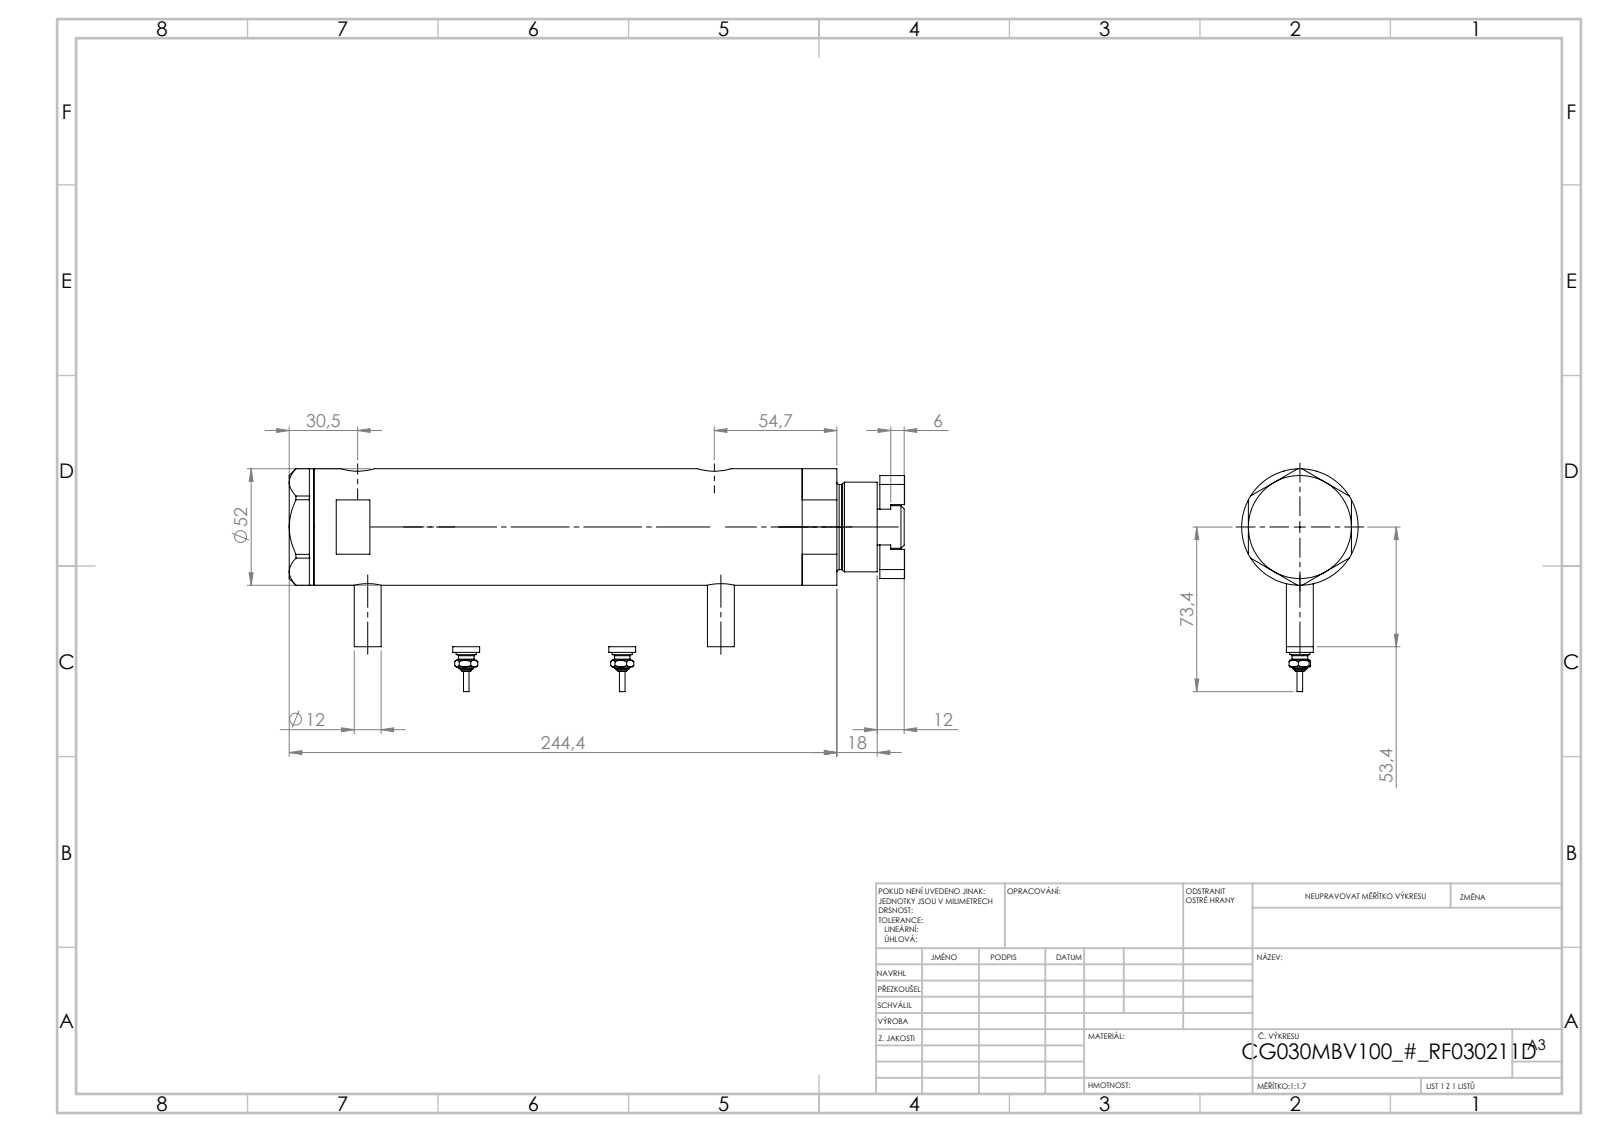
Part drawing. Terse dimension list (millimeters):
name: V270CG_VC; V270CG_BACK; V270CG_SWITCH; V270CG_FRONT (+1 more)
written by: SolidWorks 2019 (CONFIG_CONTROL_DESIGN)
unit: mm
bodies: 6 solids, 246 faces (95 planar, 77 cylindrical, 74 other)
size: 249.02 × 84.3 × 52
volume: 443 477 mm³; area: 99 080 mm²
holes: 2× ⌀5, 2× ⌀9.73, 2× ⌀12.5, 2× ⌀15, 1× ⌀6.5, 1× ⌀20, 1× ⌀21.5, 1× ⌀30, 1× ⌀33, 1× ⌀44
bosses: 3× ⌀12, 2× ⌀9, 2× ⌀7, 2× ⌀4.34, 2× ⌀2.4, 1× ⌀52, 1× ⌀40, 1× ⌀38
face distances: 153.54, 23.8, 129.74, 11, 34.8, 164.54, 46, 200.94, 189.94, 166.14
hole spacings: 2.9, 4.5, 126.75, 129.65, 131.25, 134.15, 2.89, 2.91
